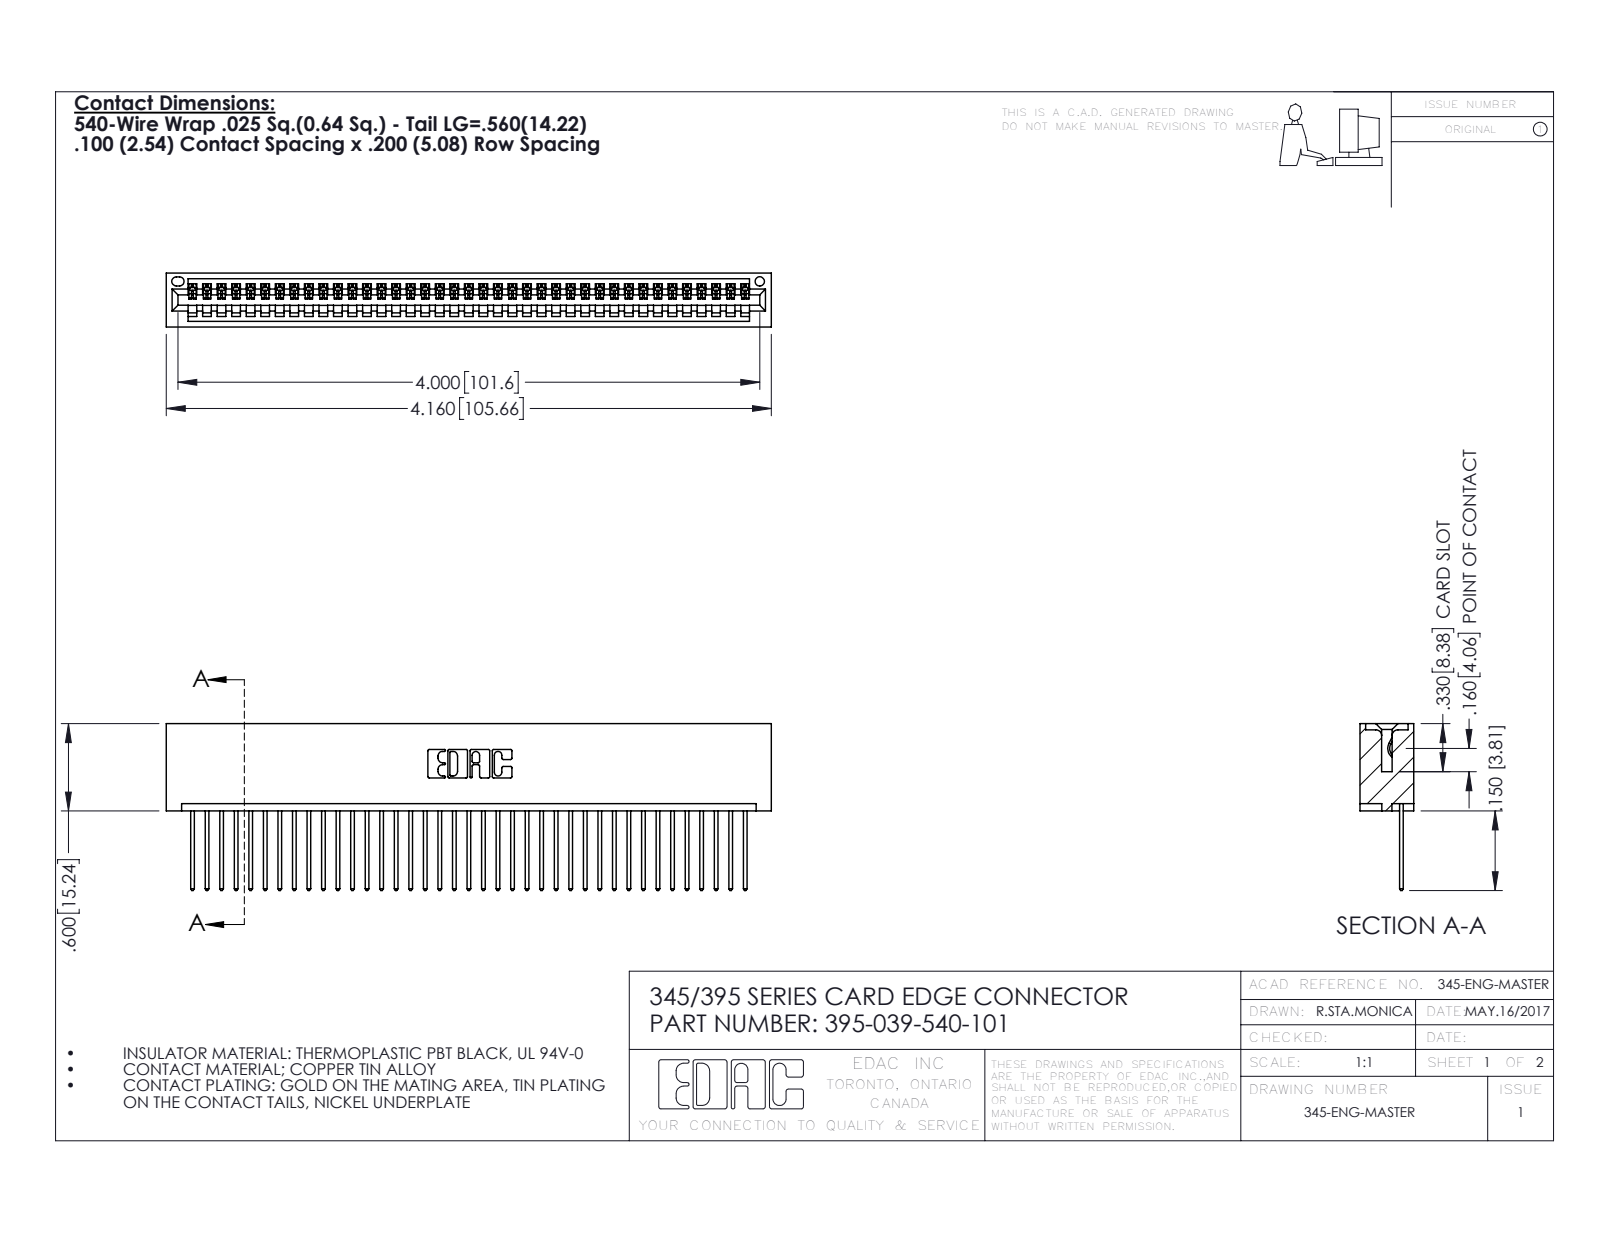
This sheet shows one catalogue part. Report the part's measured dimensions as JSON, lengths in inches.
{"part_name": "345-292-001_345-293-140; 395-039-540-101; 345 Part_No Mounting Lugs", "step_written_by": "SolidWorks 2016 (CONFIG_CONTROL_DESIGN)", "units": "inches", "bodies": {"solids": 40, "faces": 2380, "planar": 1636, "cylindrical": 744, "other": 0}, "overall_size": [4.16, 1.147, 0.37], "volume_in3": 0.65, "surface_area_in2": 22.75, "round_holes": [[0.064, 1]], "partial_cylinders_radius": [[0.006, 78], [0.01, 78], [0.01, 22], [0.007, 6], [0.031, 6], [0.026, 3], [0.031, 2], [0.04, 2]], "face_to_face_distances": [0.072, 0.298, 0.098, 0.272, 0.025, 0.37, 0.2, 0.225, 0.149, 0.072]}
